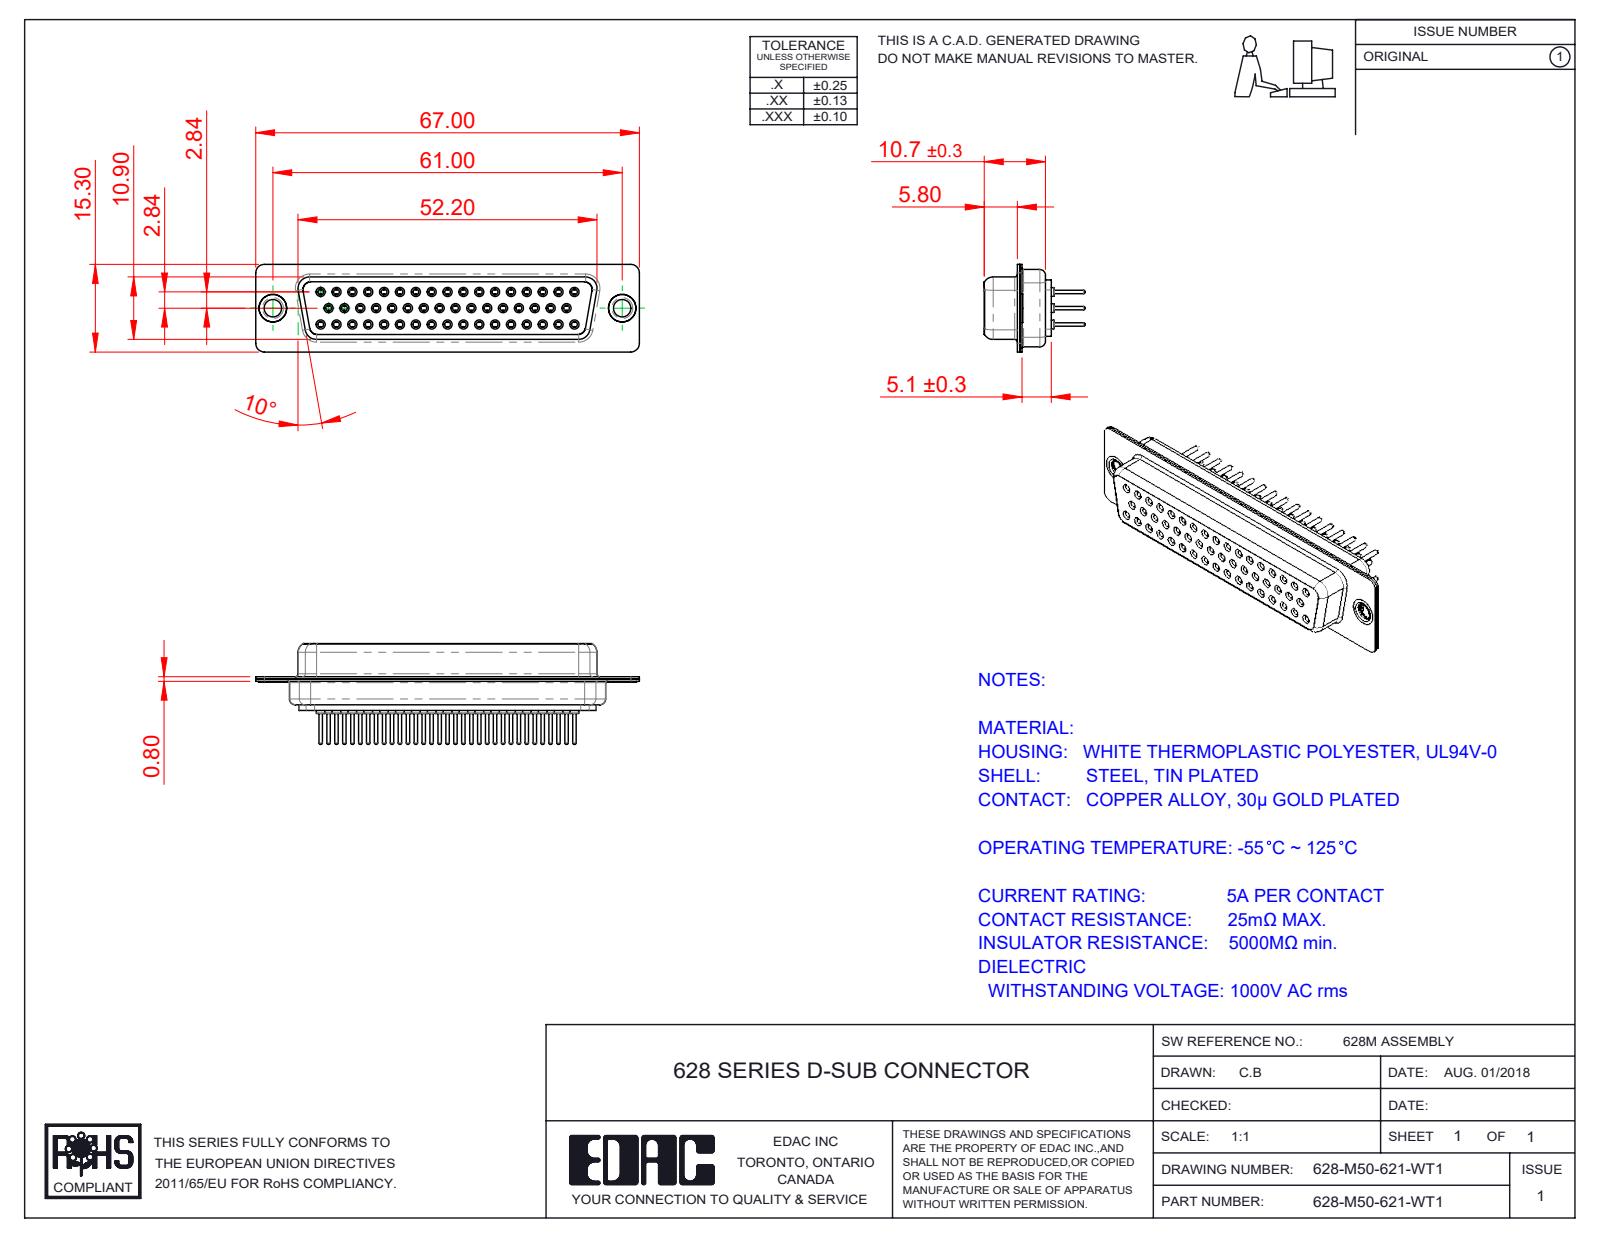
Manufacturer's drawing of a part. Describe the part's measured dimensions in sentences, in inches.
The part is named "628M Shell Rear_50 Contacts; 628M Contact Row 3_21; 628M Contact Row 1_21; 628-M50-621-WT1 (+4 more)". Its 3-D file was written by "SolidWorks 2020 (CONFIG_CONTROL_DESIGN)". It is 55 solids with 3003 faces: 817 planar, 1071 cylindrical and 1115 other. Overall it measures 2.638 by 0.693 by 0.602 inches. Its volume is 0.399 cubic inches and its surface area 23.08 square inches. Round holes: 50 of diameter 0.039, 50 of diameter 0.043, 50 of diameter 0.067, 50 of diameter 0.071, 50 of diameter 0.079, 2 of diameter 0.12, 2 of diameter 0.157, 2 of diameter 0.189. Round bosses or shafts: 50 of diameter 0.087, 50 of diameter 0.063, 50 of diameter 0.059, 50 of diameter 0.024, 2 of diameter 0.197, 2 of diameter 0.193, 2 of diameter 0.14. Partial cylindrical surfaces (rounded edges, fillets, slot ends): 16 of radius 0.059, 12 of radius 0.079, 8 of radius 0.053, 8 of radius 0.063, 4 of radius 0.01, 4 of radius 0.02, 4 of radius 0.024, 4 of radius 0.026. The main face-to-face distances are 0.016, 0.051, 0.465, 0.035, 0.217, 0.232, 0.033, 0.516, 0.228, 0.396. The hole center spacings are 0.124, 0.109, 0.218, 0.327, 0.436, 0.545, 0.654, 0.763.
